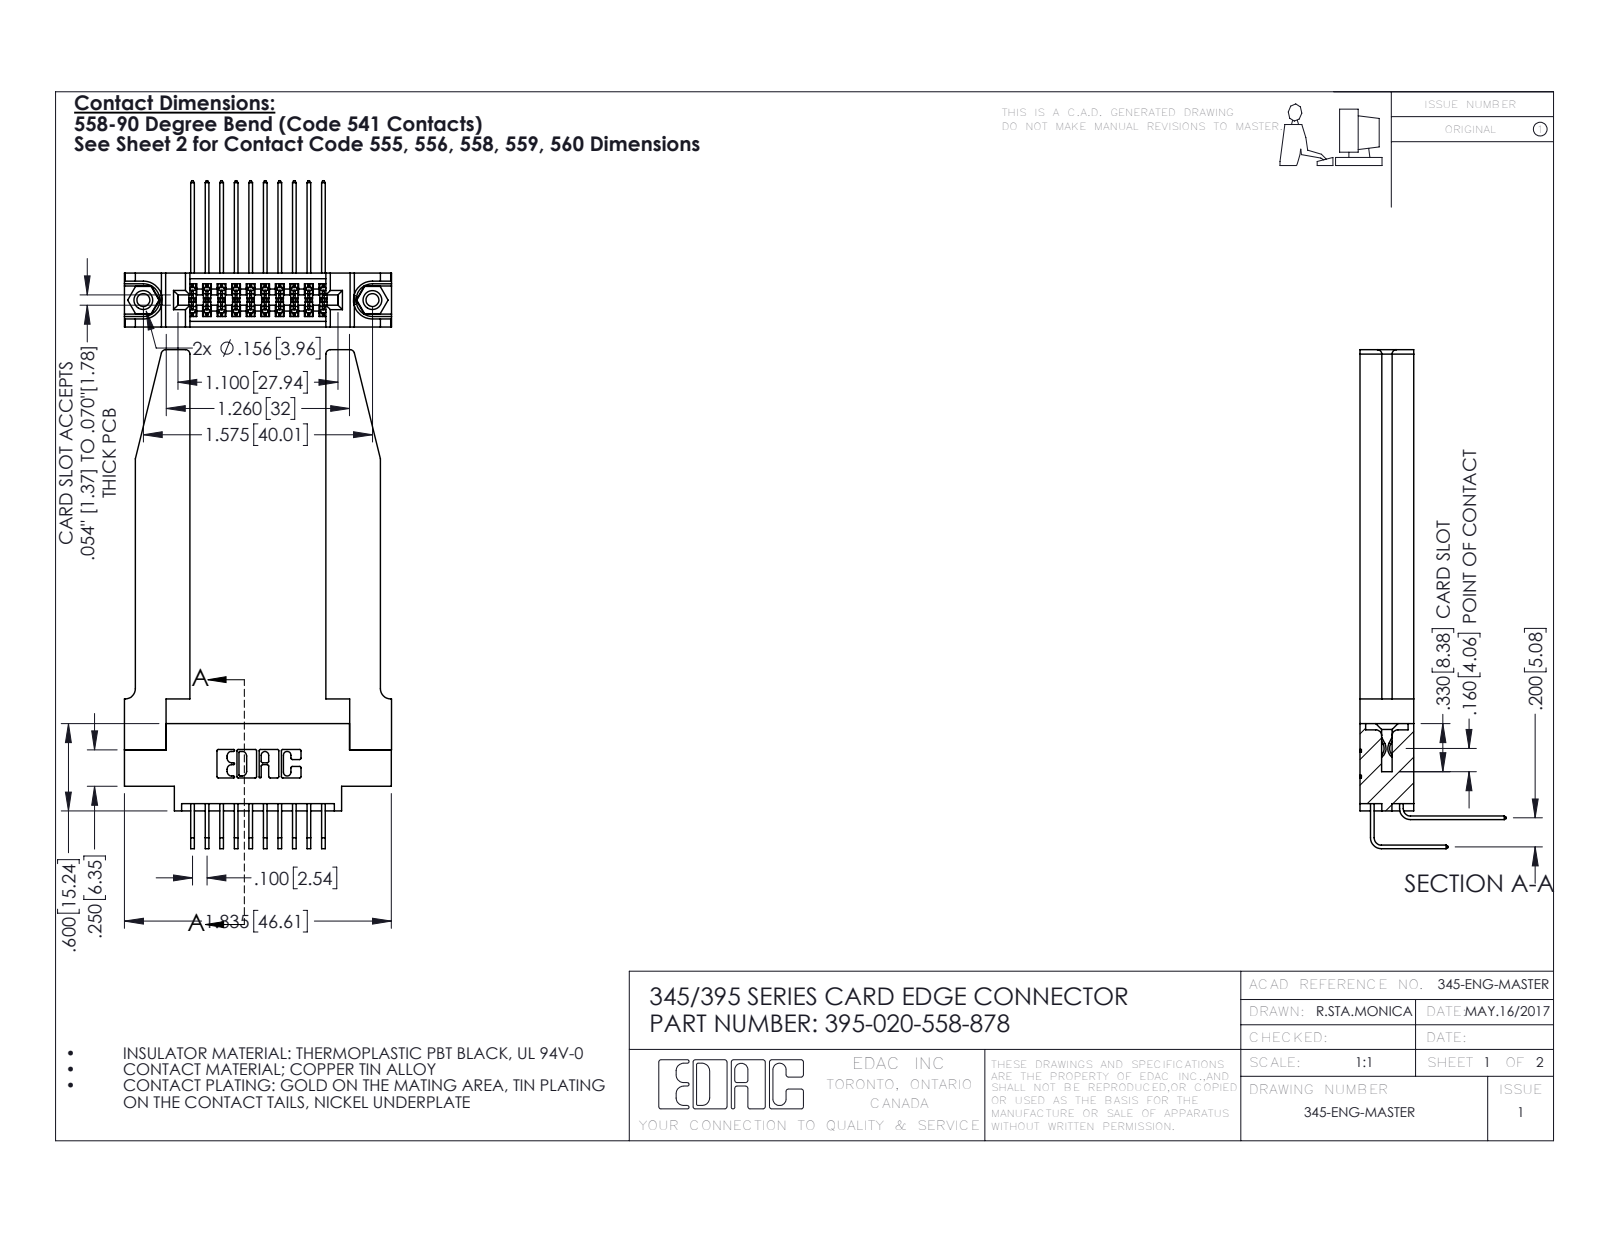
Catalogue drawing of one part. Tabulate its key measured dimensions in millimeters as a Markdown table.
| quantity | value |
| --- | --- |
| part name | 345-250-001_345-250-001-102; 345-292-001_558 559 Tail - 1; 345-220-078_345-220-078; 395-020-558-878 (+2 more) |
| STEP written by | SolidWorks 2016 (CONFIG_CONTROL_DESIGN) |
| units | millimeters |
| bodies | 25 solids, 1404 faces (926 planar, 426 cylindrical, 52 other) |
| overall size | 87.1 × 46.6 × 25.5 |
| volume | 12 000 mm³ |
| surface area | 13 170 mm² |
| round holes (diameter × count) | 2.3 × 2, 3.2 × 2, 4 × 2, 1.6 × 1 |
| round bosses / shafts (diameter × count) | 3.9 × 2 |
| partial cylindrical surfaces (radius × count) | 0.2 × 31, 0.3 × 22, 0.8 × 8, 0.2 × 6, 0.8 × 6, 0.7 × 3, 0.4 × 2, 0.5 × 2 |
| main face-to-face distances | 9.4, 1.8, 7.6, 3.8, 3.8, 5.1, 5.6, 2, 23.7, 2.5 |
| hole center spacings | 6.9, 34.1, 40 |
